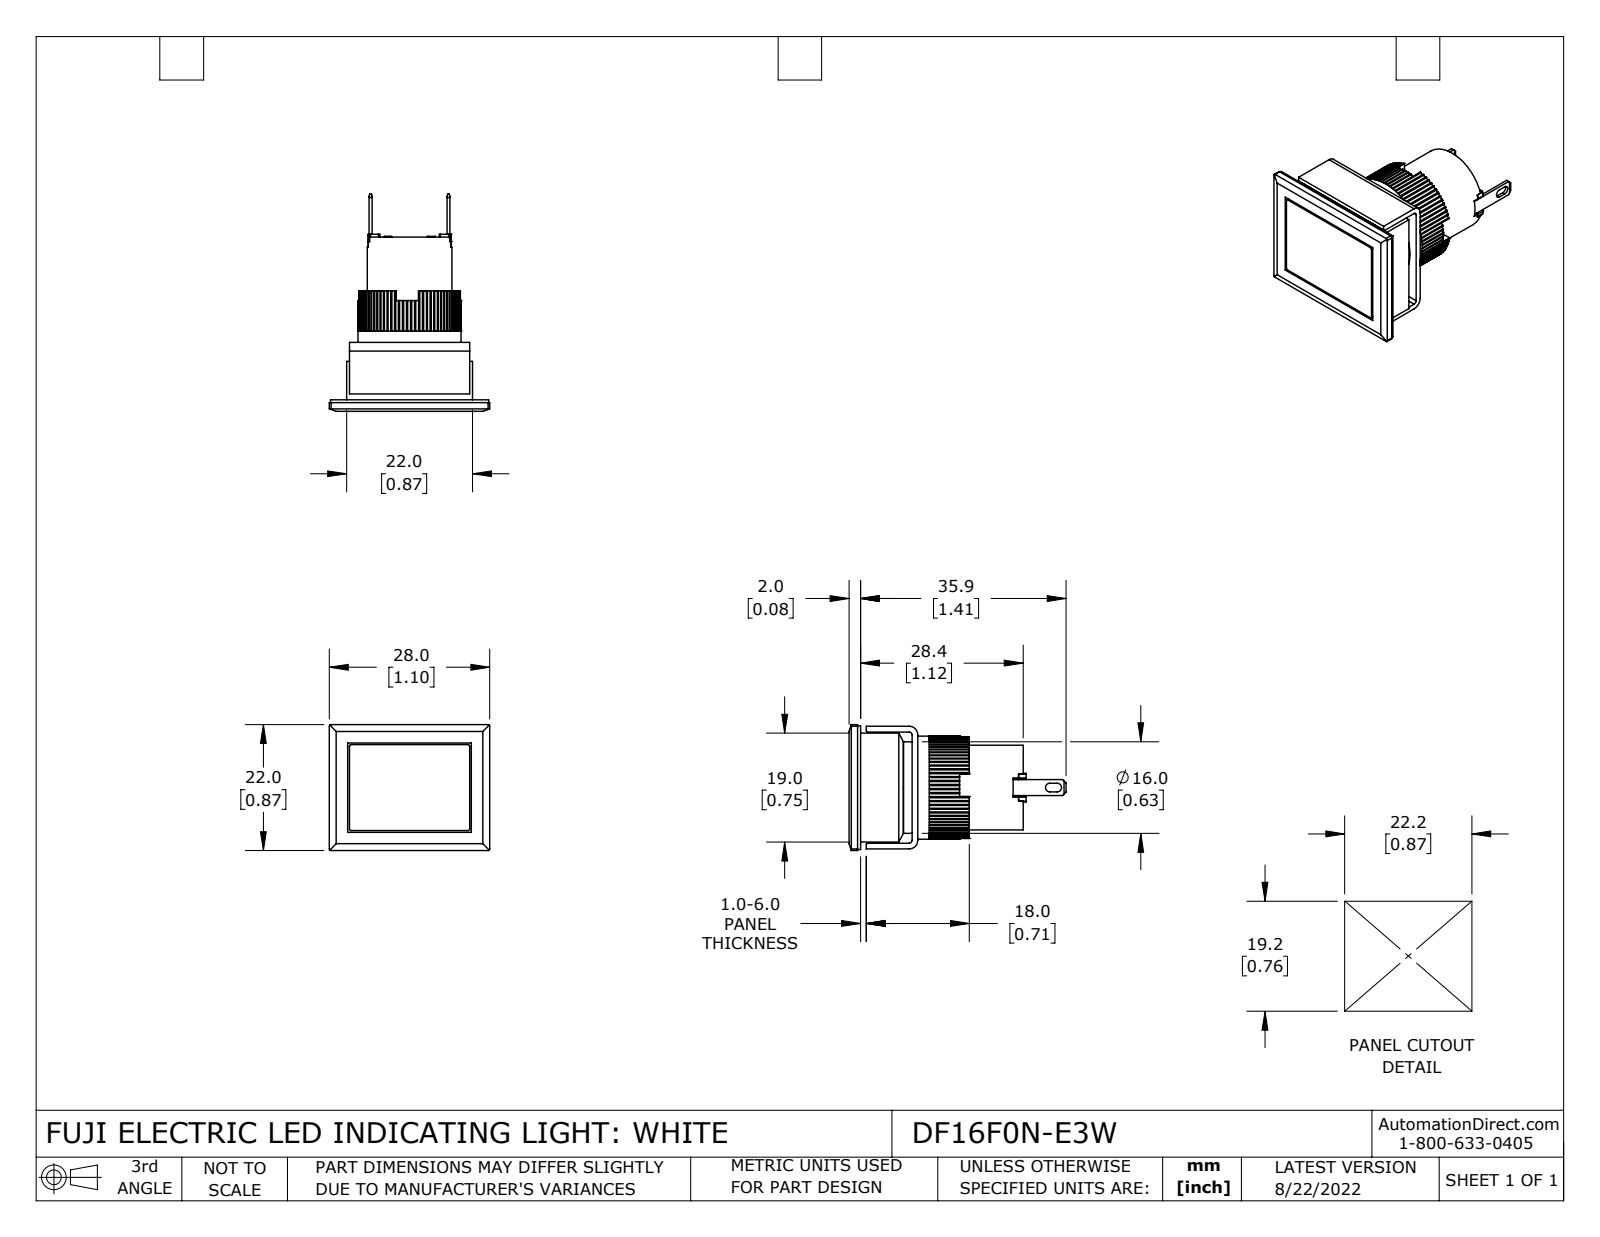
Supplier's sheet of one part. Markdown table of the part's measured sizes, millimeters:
| quantity | value |
| --- | --- |
| part name | DF16F0N-E3W |
| STEP written by | SolidWorks 2021 (CONFIG_CONTROL_DESIGN) |
| units | millimeters |
| bodies | 10 solids, 495 faces (312 planar, 181 cylindrical, 2 other) |
| overall size | 37.9 × 28 × 22 |
| volume | 8 950 mm³ |
| surface area | 7 535 mm² |
| round holes (diameter × count) | 1 × 1, 18 × 1 |
| round bosses / shafts (diameter × count) | 16 × 1, 14.8 × 1 |
| partial cylindrical surfaces (radius × count) | 0.3 × 80, 0.2 × 12, 0.3 × 8, 0.5 × 2, 0.8 × 2, 1.5 × 2 |
| main face-to-face distances | 1.5, 9.5, 3.6, 0.5, 1, 8, 5.9, 2.1, 2, 19.2 |
